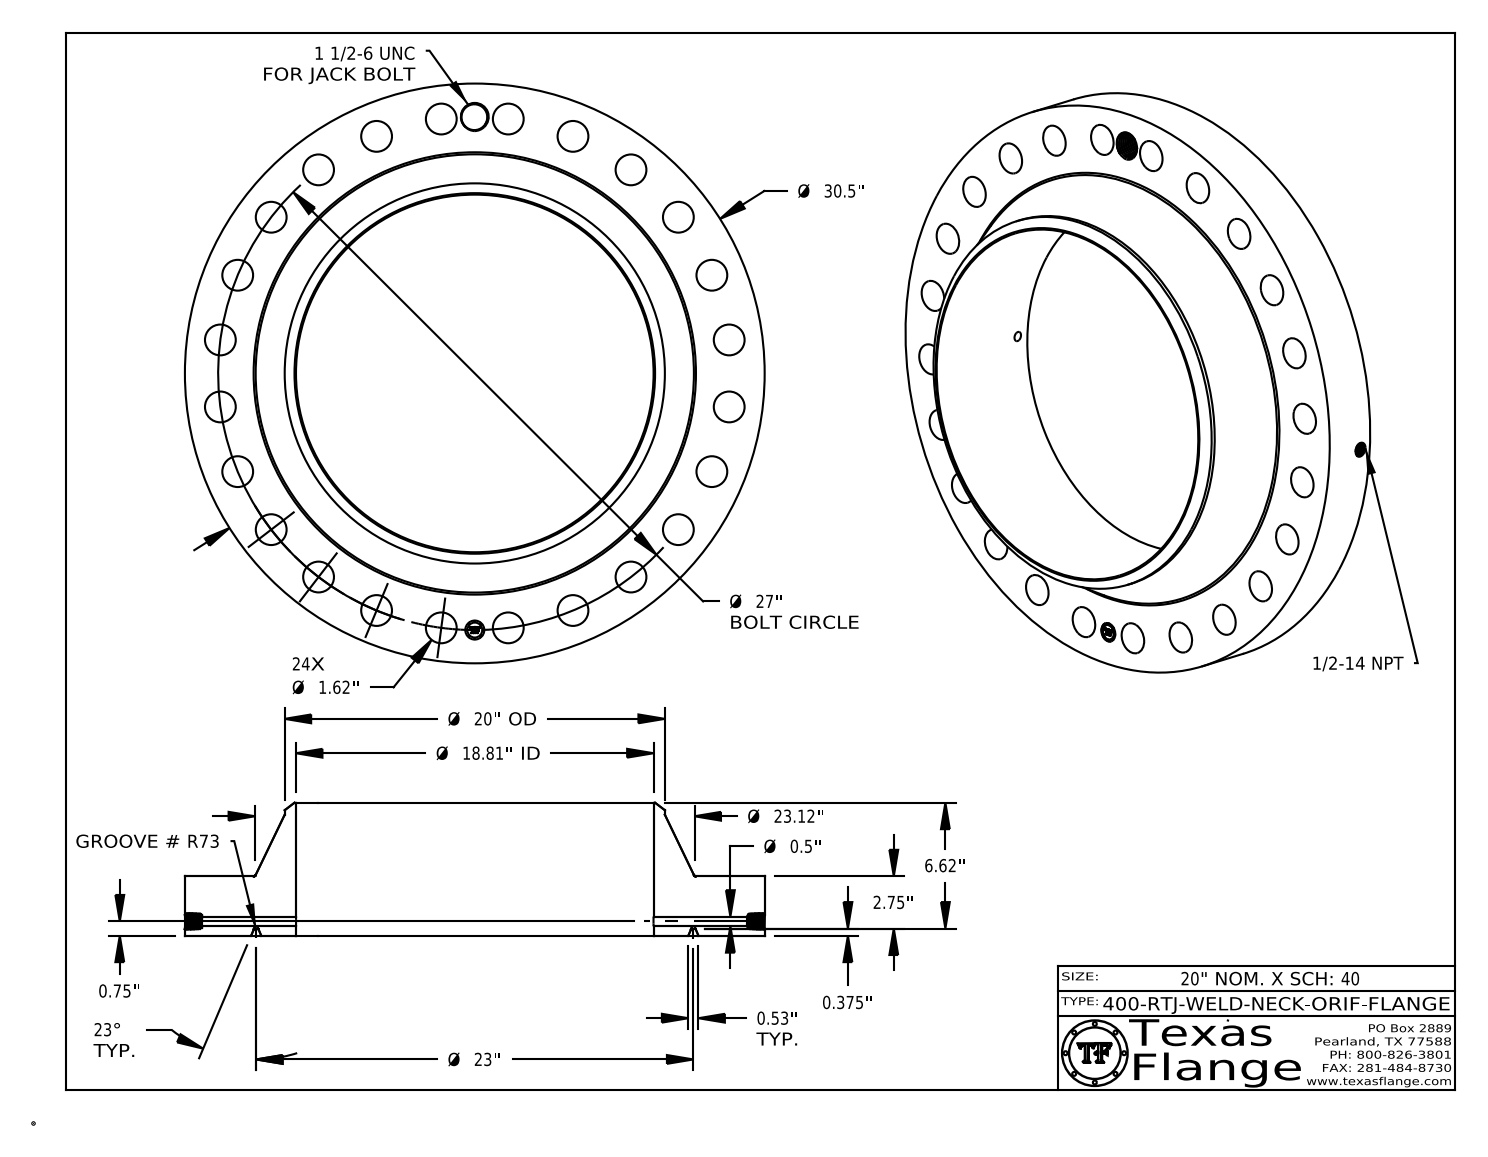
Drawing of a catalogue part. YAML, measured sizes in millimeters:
part_name: "400-RTJ-WELD-NECK"
step_written_by: "CATIA V5 STEP AP214 (AUTOMOTIVE_DESIGN)"
units: millimeters
bodies: {solids: 1, faces: 831, planar: 370, cylindrical: 131, other: 330}
overall_size: [774.7, 774.7, 177.7]
volume: 25290000
surface_area: 1376000
round_holes:
  - {diameter: 41.1, count: 24}
  - {diameter: 12.7, count: 1}
  - {diameter: 17.1, count: 1}
  - {diameter: 25.4, count: 1}
  - {diameter: 34.1, count: 1}
  - {diameter: 477.8, count: 1}
round_bosses_or_shafts:
  - {diameter: 1.5, count: 8}
  - {diameter: 774.7, count: 1}
  - {diameter: 508, count: 1}
  - {diameter: 20, count: 1}
face_to_face_distances: [79.4, 9.5, 69.9, 177.7, 168.1, 98.3, 0.4, 79, 69.5, 98.7]
hole_center_spacings: [342.9, 593.9, 633.6, 544.1, 89.5, 177.5, 484.9, 662.4]
